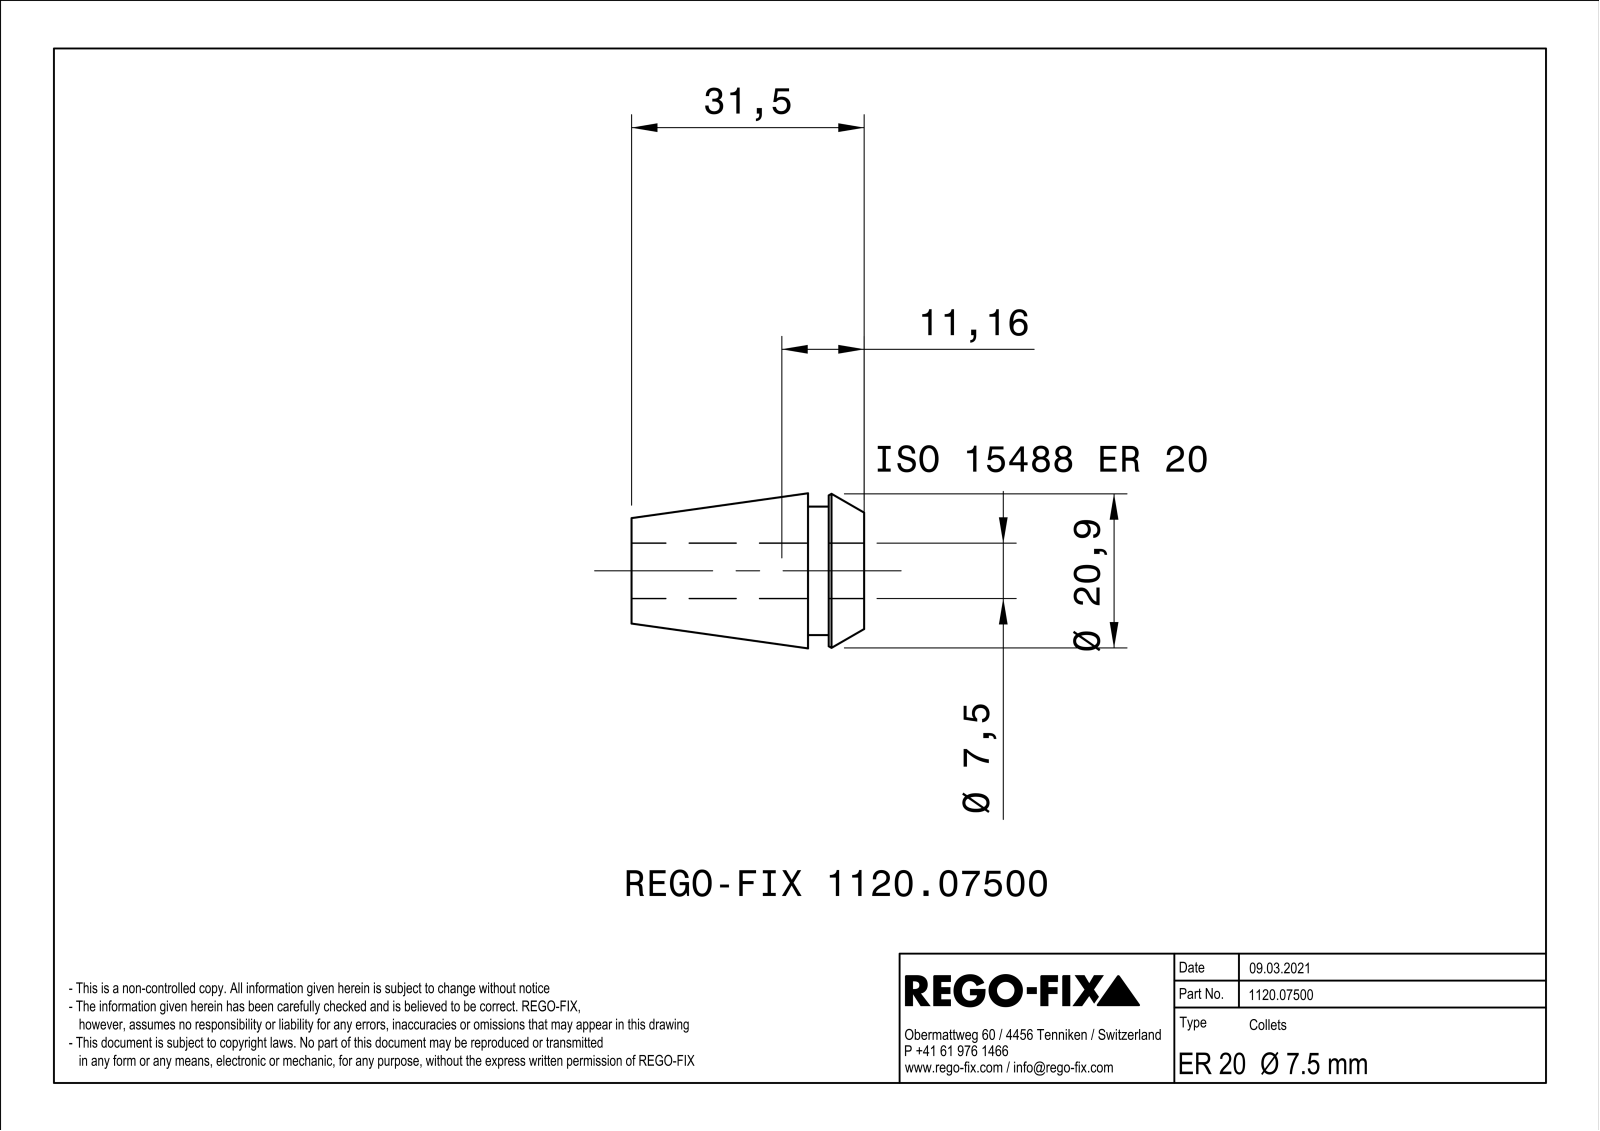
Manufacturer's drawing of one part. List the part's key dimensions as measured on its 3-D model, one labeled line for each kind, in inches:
Part name (STEP PRODUCT): NOCUT
STEP written by: SIEMENS PLM Software Solid Edge ST10 (AUTOMOTIVE_DESIGN)
Units: inches
Bodies: 1 solid, 177 faces (88 planar, 9 cylindrical, 80 other)
Overall size (bounding box): 1.24 × 0.826 × 0.826
Volume: 0.312 in³ · Surface area: 10.85 in²
Round holes (diameter × count): ⌀0.295 ×1
Round bosses / shafts (diameter × count): ⌀0.685 ×1
Main face-to-face distances: 0.024, 1.24, 0.299, 0.941, 0.189, 0.11, 1.051, 0.217, 0.028, 0.083
